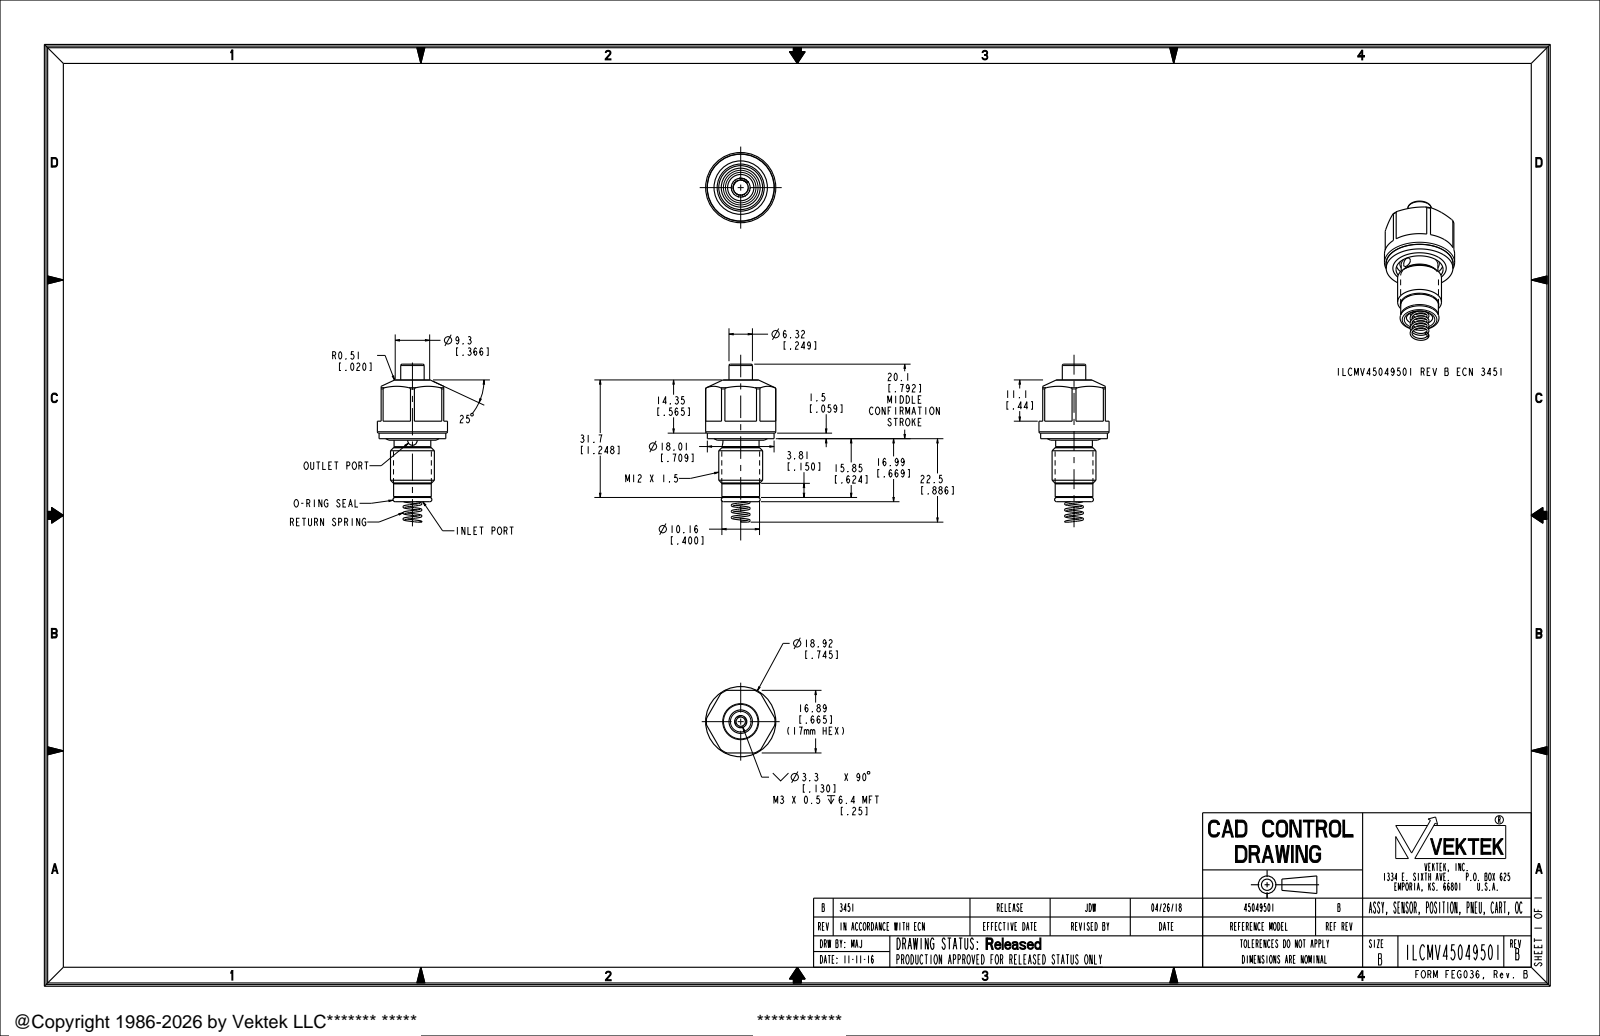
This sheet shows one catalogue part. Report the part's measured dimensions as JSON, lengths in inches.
{"part_name": "ILCMV45049501", "step_written_by": "PRO/ENGINEER BY PARAMETRIC TECHNOLOGY CORPORATION, 2013320 (AUTOMOTIVE_DESIGN)", "units": "inches", "bodies": {"solids": 1, "faces": 92, "planar": 26, "cylindrical": 24, "other": 42}, "overall_size": [1.678, 0.745, 0.745], "volume_in3": 0.308, "surface_area_in2": 4.847, "round_holes": [[0.098, 1], [0.1, 1], [0.118, 1], [0.312, 1], [0.5, 1]], "round_bosses_or_shafts": [[0.745, 1], [0.709, 1], [0.466, 1], [0.402, 1], [0.4, 1], [0.39, 1], [0.249, 1]], "face_to_face_distances": [0.665, 0.324, 0.624, 0.383, 0.059, 0.948, 0.565, 0.51, 0.186, 0.127]}
